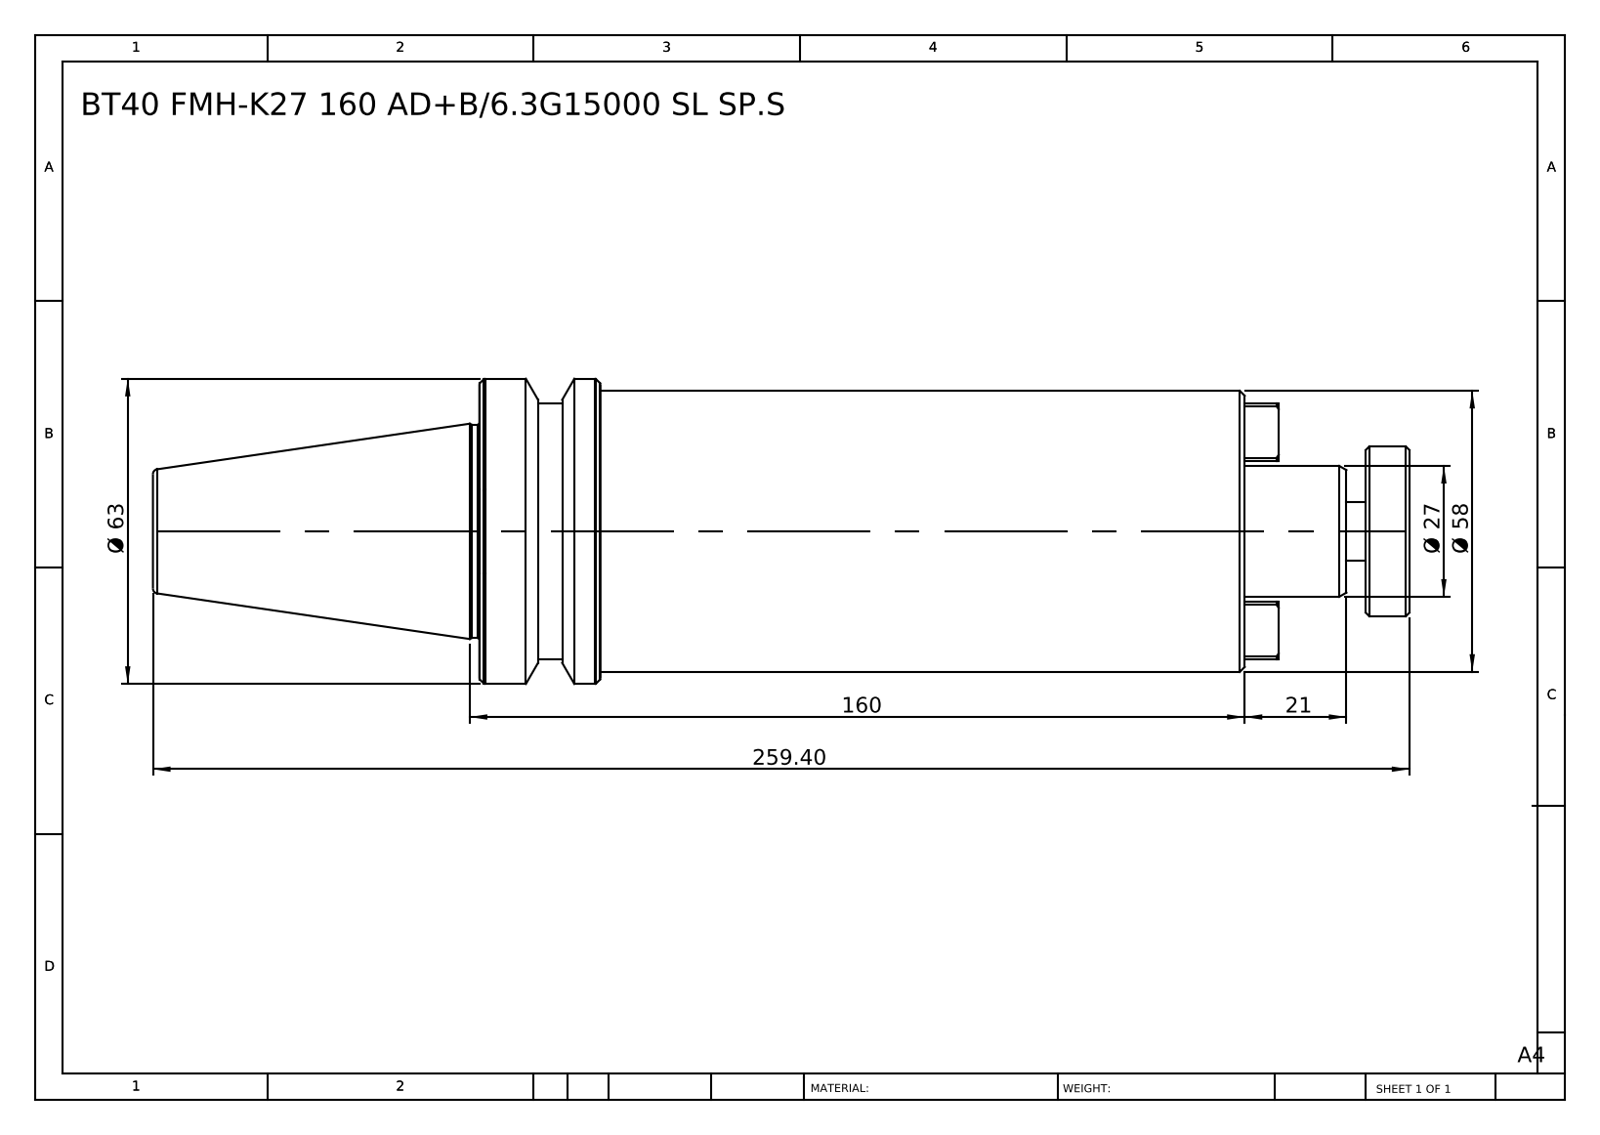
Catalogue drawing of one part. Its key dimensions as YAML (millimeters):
part_name: "BT40 FMH27 160 AD-6.3G 15000 SL SP"
step_written_by: "SolidWorks 2014 (CONFIG_CONTROL_DESIGN)"
units: millimeters
bodies: {solids: 1, faces: 89, planar: 35, cylindrical: 16, other: 38}
overall_size: [259.4, 63, 63]
volume: 512755
surface_area: 47571
round_bosses_or_shafts:
  - {diameter: 63, count: 1}
  - {diameter: 58, count: 1}
  - {diameter: 53, count: 1}
  - {diameter: 44, count: 1}
  - {diameter: 35, count: 1}
  - {diameter: 27, count: 1}
  - {diameter: 12, count: 1}
face_to_face_distances: [158, 25, 34, 192, 9, 183, 259.4, 250.4, 225.4, 67.4]
